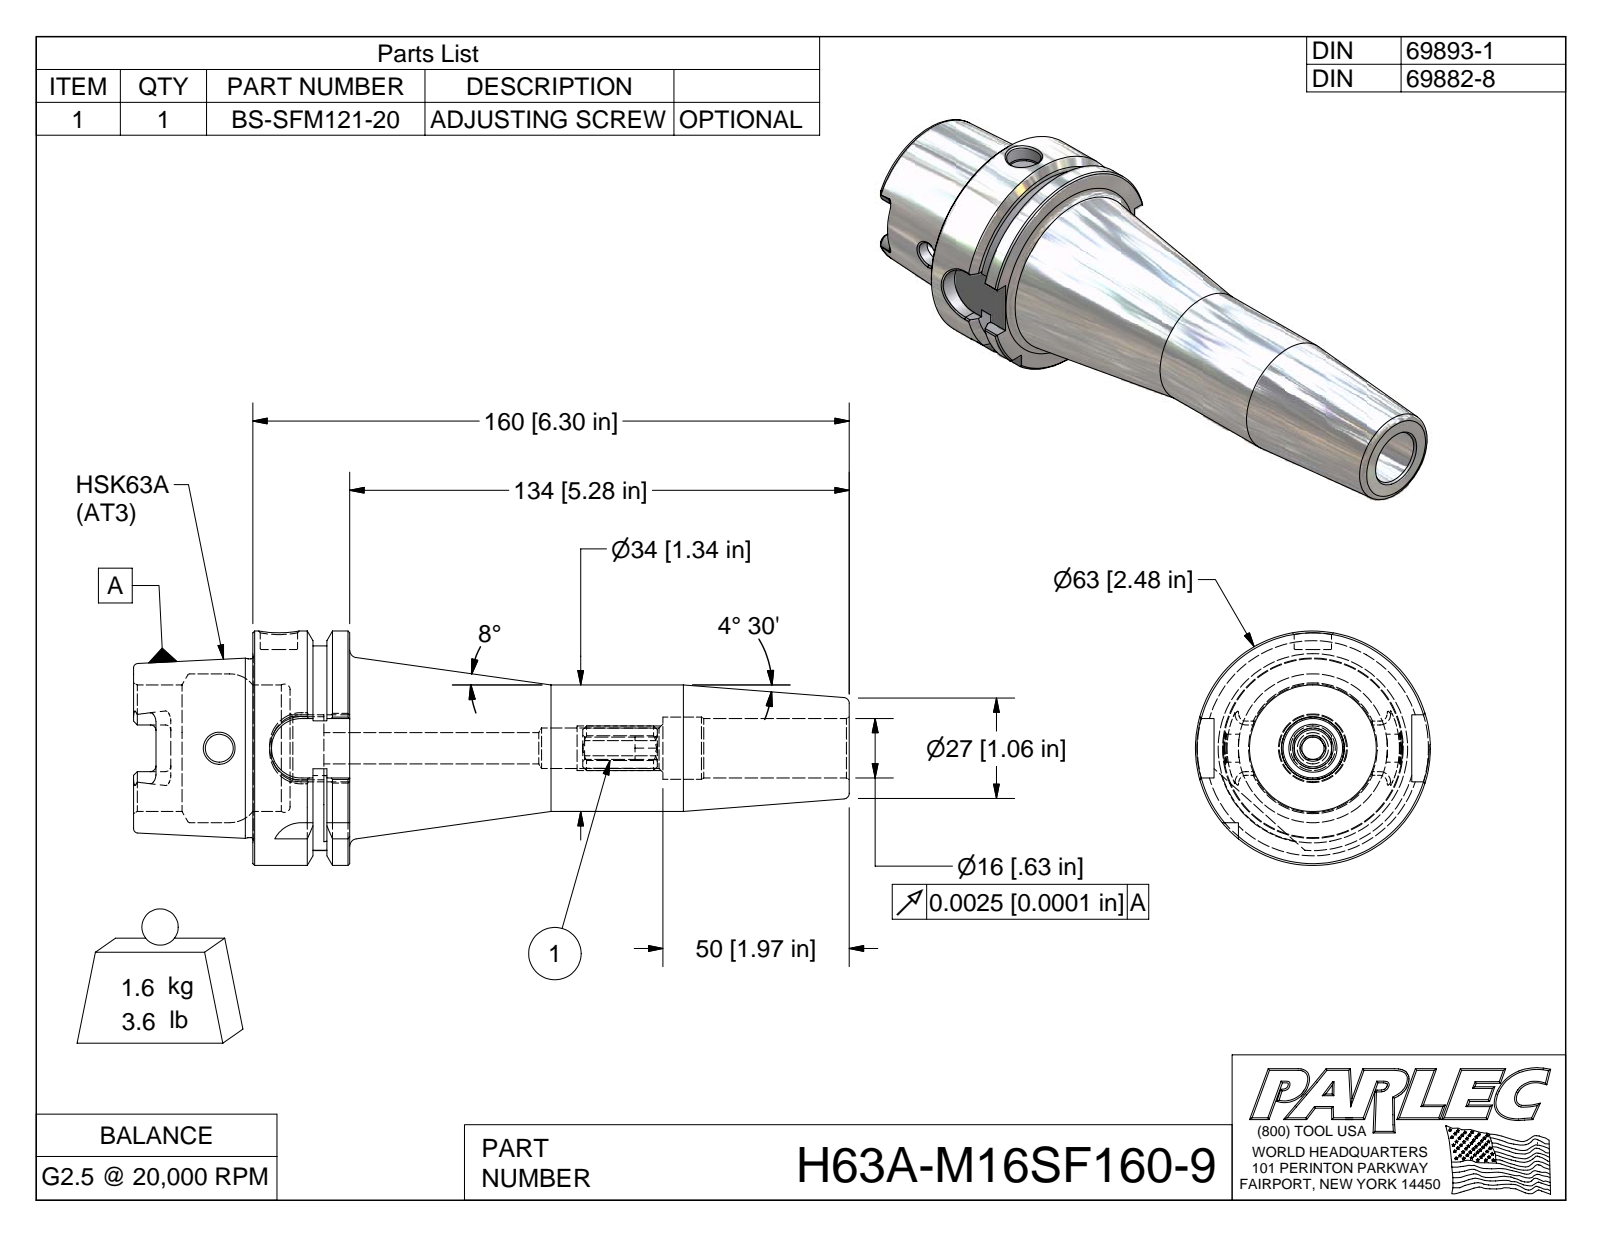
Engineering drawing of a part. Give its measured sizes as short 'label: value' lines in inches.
name: H63A-M16SF160-9; H63A-M16SF160-9-1; BS-SFM121-20
written by: Autodesk Inventor 2009 (AUTOMOTIVE_DESIGN)
unit: in
bodies: 2 solids, 160 faces (59 planar, 35 cylindrical, 66 other)
size: 7.559 × 2.48 × 2.48
volume: 12.58 in³; area: 65.48 in²
holes: 1× ⌀0.295, 1× ⌀0.394, 1× ⌀0.629, 1× ⌀0.659, 1× ⌀0.666, 1× ⌀1.339, 1× ⌀1.575
bosses: 1× ⌀2.48, 1× ⌀1.891
rounds: 6× R0.059, 4× R0.113, 4× R0.315, 1× R0.236, 1× R1.083
face distances: 1.024, 0.394, 0.241, 0.389, 0.63, 1.26, 1.654, 2.283, 1.894, 0.635
